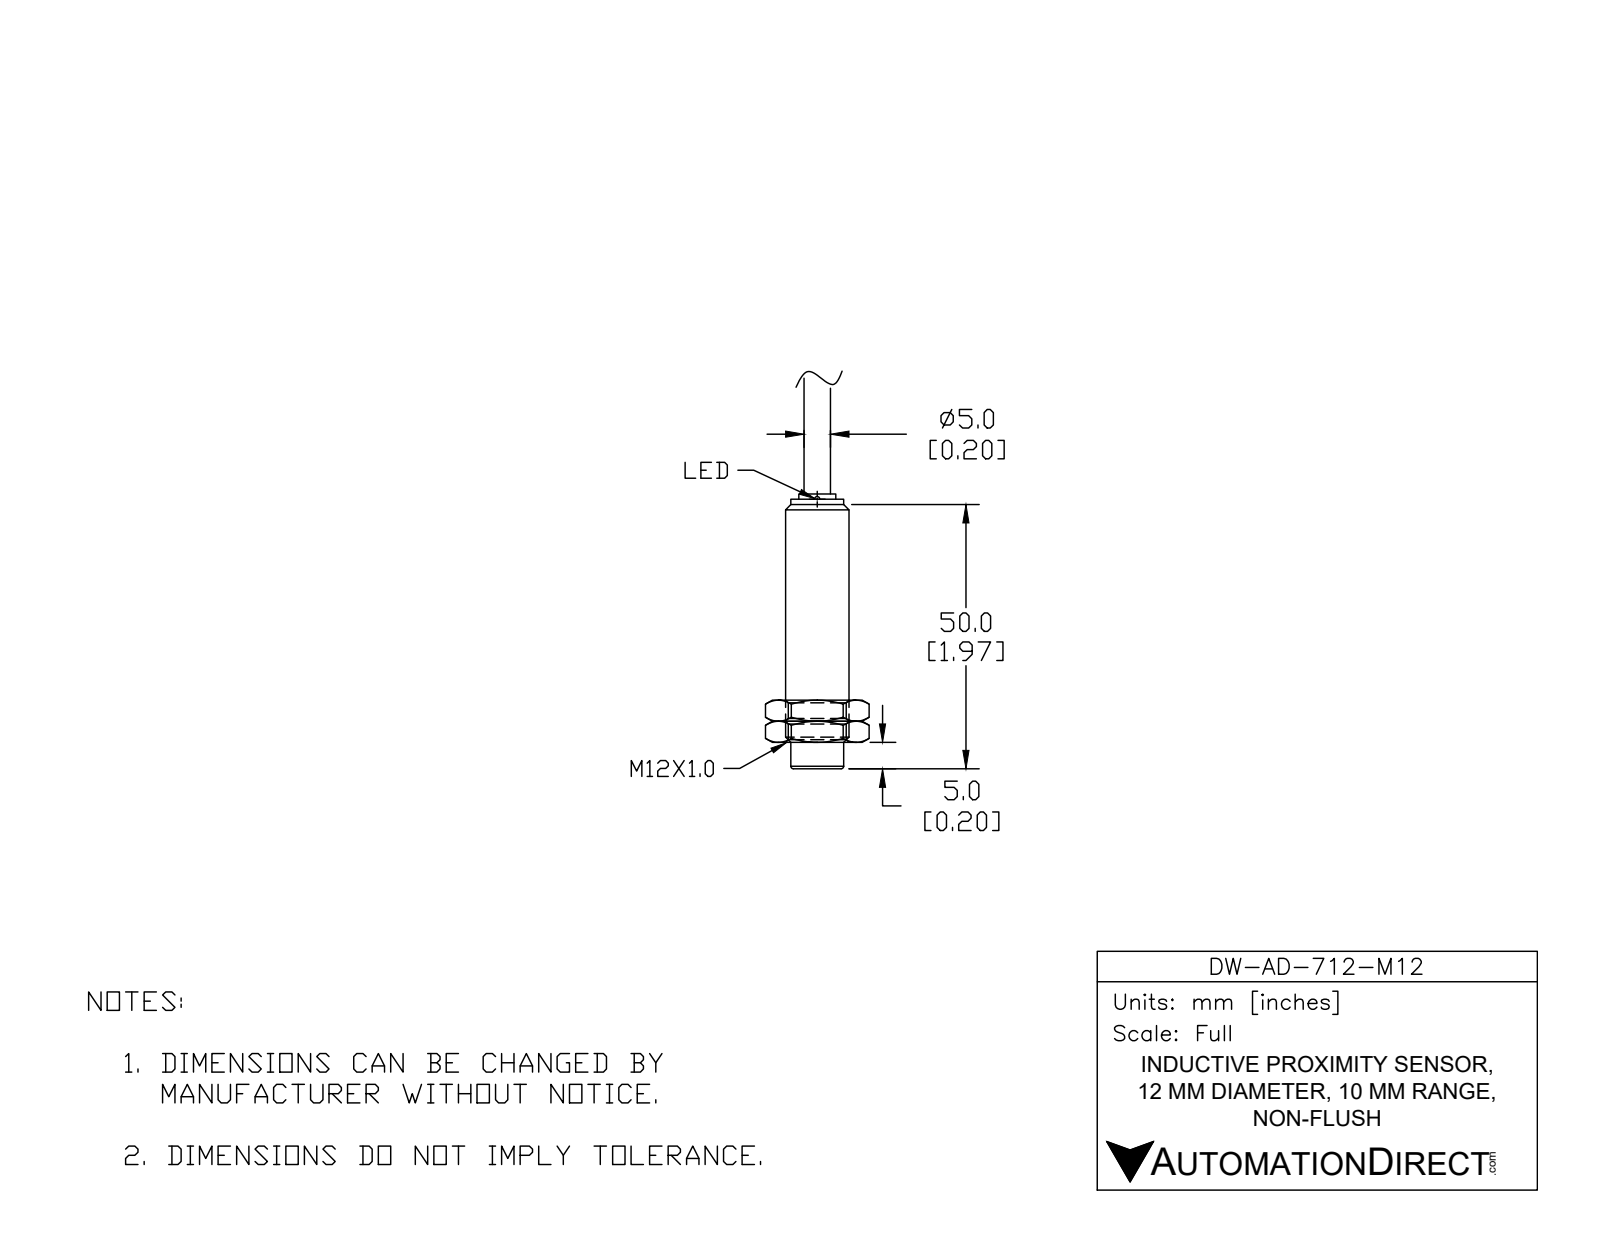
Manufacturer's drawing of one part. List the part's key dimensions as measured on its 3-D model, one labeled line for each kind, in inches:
Part name (STEP PRODUCT): DW-AD-712-M12
STEP written by: SolidWorks 2017 (AUTOMOTIVE_DESIGN)
Units: inches
Bodies: 2 solids, 34 faces (17 planar, 6 cylindrical, 11 other)
Overall size (bounding box): 2.976 × 0.472 × 0.472
Volume: 0.377 in³ · Surface area: 4.017 in²
Round bosses / shafts (diameter × count): ⌀0.472 ×1, ⌀0.415 ×1, ⌀0.413 ×1, ⌀0.268 ×1, ⌀0.197 ×1, ⌀0.118 ×1
Main face-to-face distances: 2.047, 2, 0.047, 1.85, 0.15, 0.197, 2.031, 0.181, 0.031, 0.016
